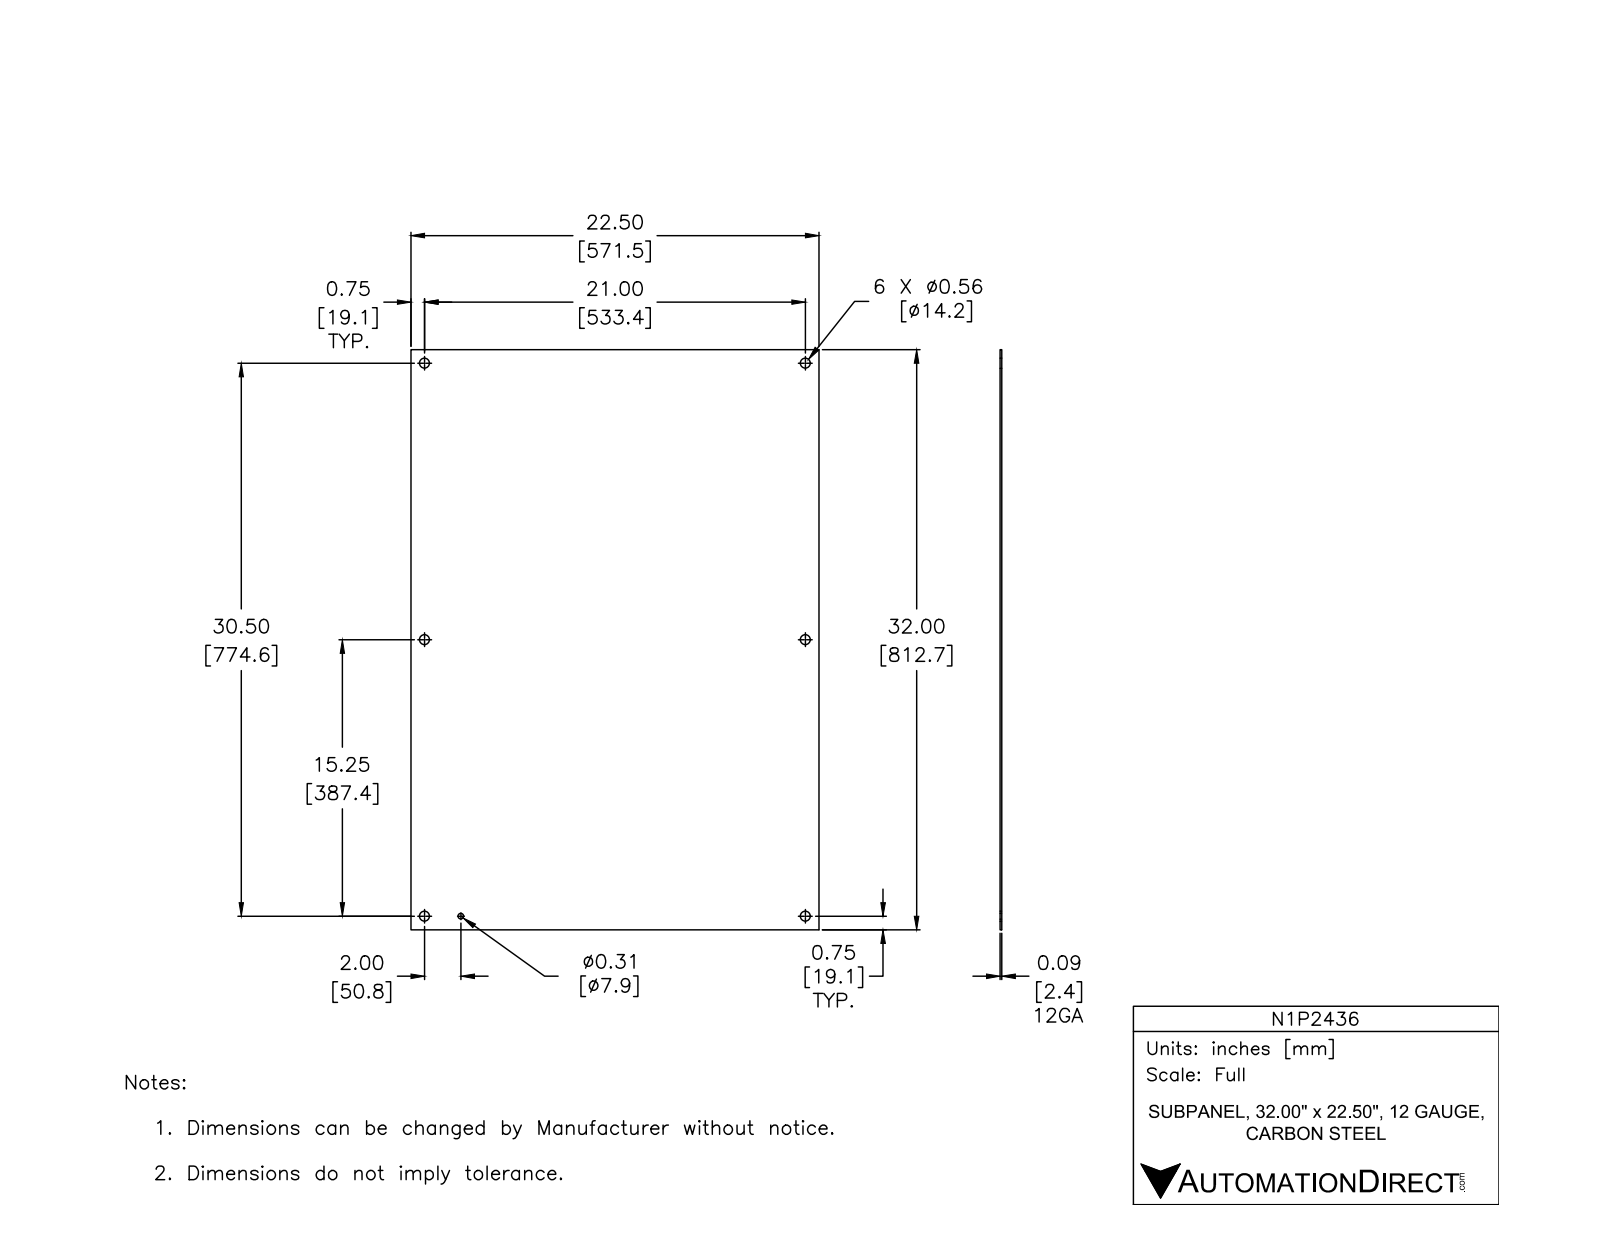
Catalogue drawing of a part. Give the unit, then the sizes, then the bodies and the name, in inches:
Units: inches
Overall size (bounding box): 32 × 22.5 × 0.094
Round holes (diameter × count): ⌀0.563 ×6, ⌀0.312 ×1
Main face-to-face distances: 0.094, 22.5, 32
Hole centre spacings: 15.25, 25.953, 21, 30.5, 37.03, 2, 15.381, 19
Volume: 67.35 in³ · Surface area: 1 448 in²
Bodies: 1 solid, 13 faces (6 planar, 7 cylindrical, 0 other)
Part name (STEP PRODUCT): N1P2436-1
STEP written by: Autodesk Inventor 2012 (AUTOMOTIVE_DESIGN)
